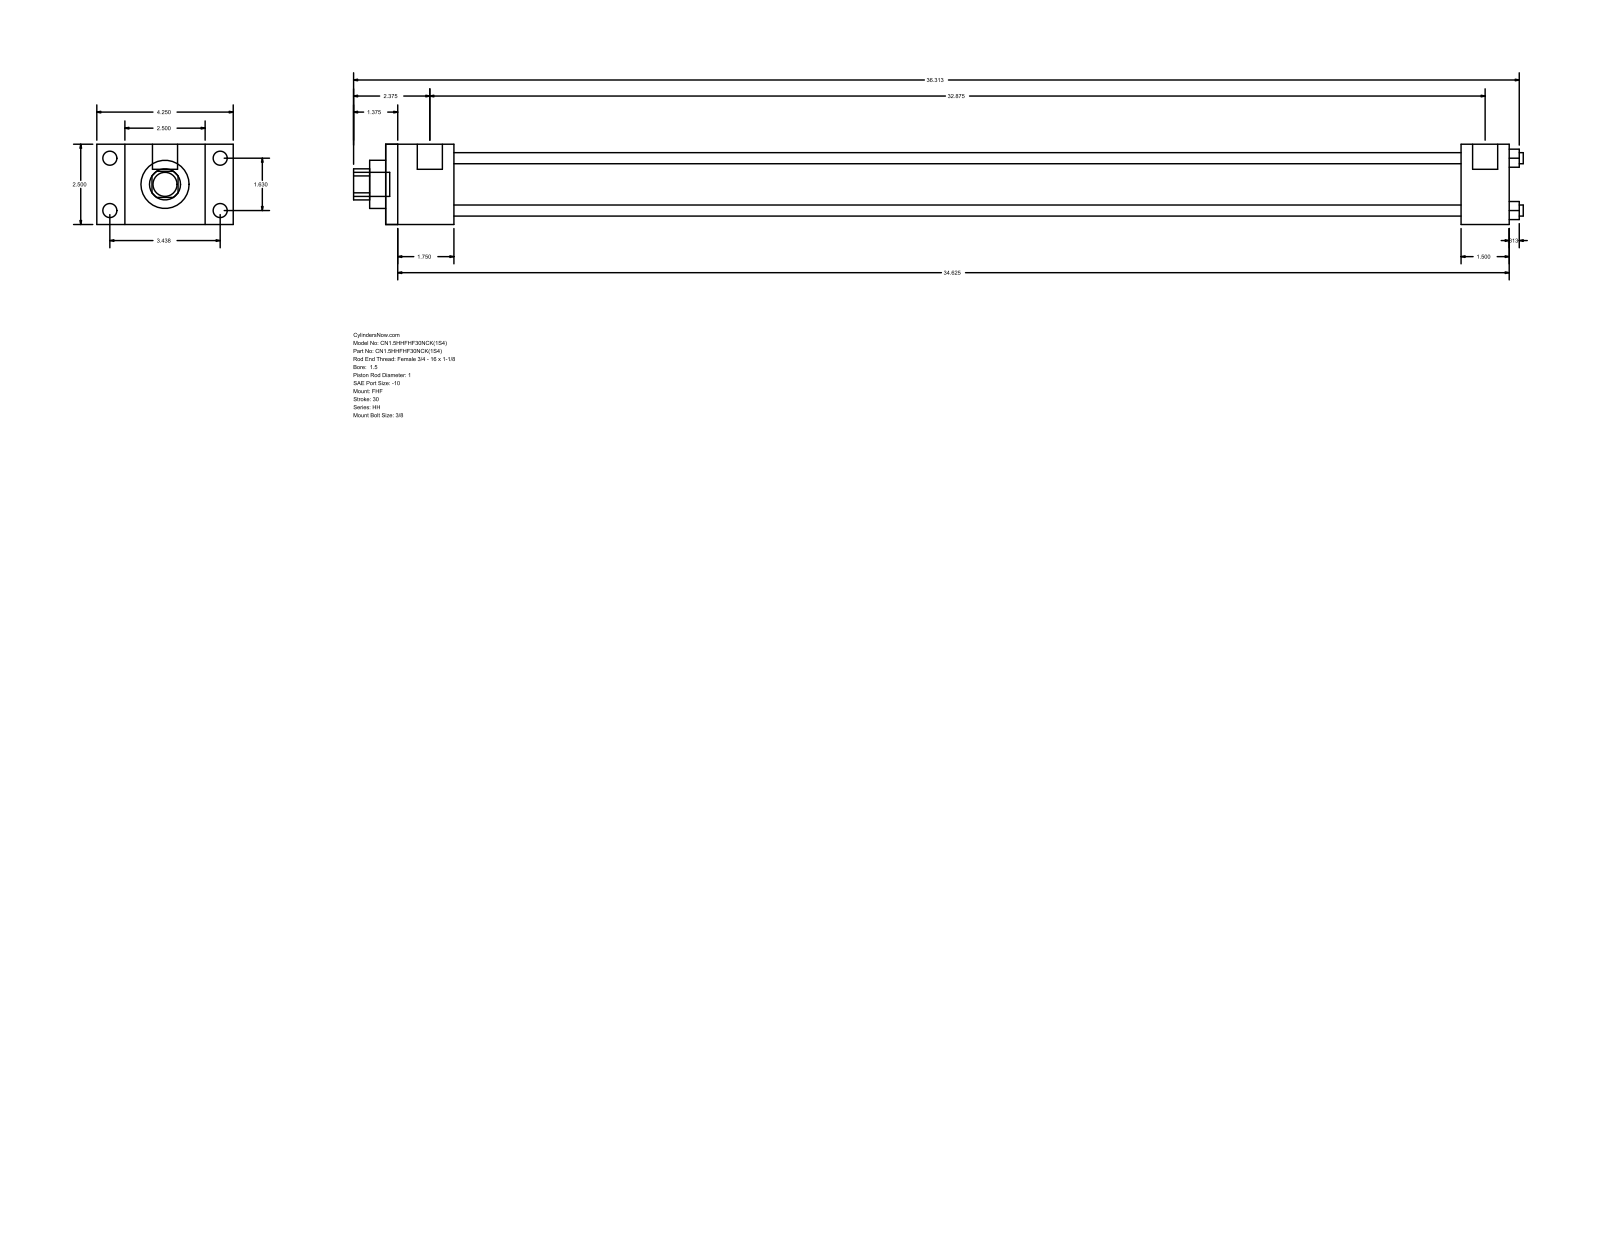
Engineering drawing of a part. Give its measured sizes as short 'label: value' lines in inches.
name: HH_FHF__0150_1
written by: GSSL Pune (CONFIG_CONTROL_DESIGN)
unit: in
bodies: 0 solids, 88 faces (60 planar, 28 cylindrical, 0 other)
size: 36.437 × 4.25 × 2.5
holes: 4× ⌀0.345, 1× ⌀1, 1× ⌀1.5, 1× ⌀1.75
bosses: 4× ⌀0.438, 4× ⌀0.219, 2× ⌀0.781, 1× ⌀0.75
rounds: 1× R0.484
face distances: 2.5, 0.875, 3.375, 2.125, 4.25, 35, 32.875, 33.5, 31.375, 1.5
hole spacings: 1.152, 1.63, 2.305
